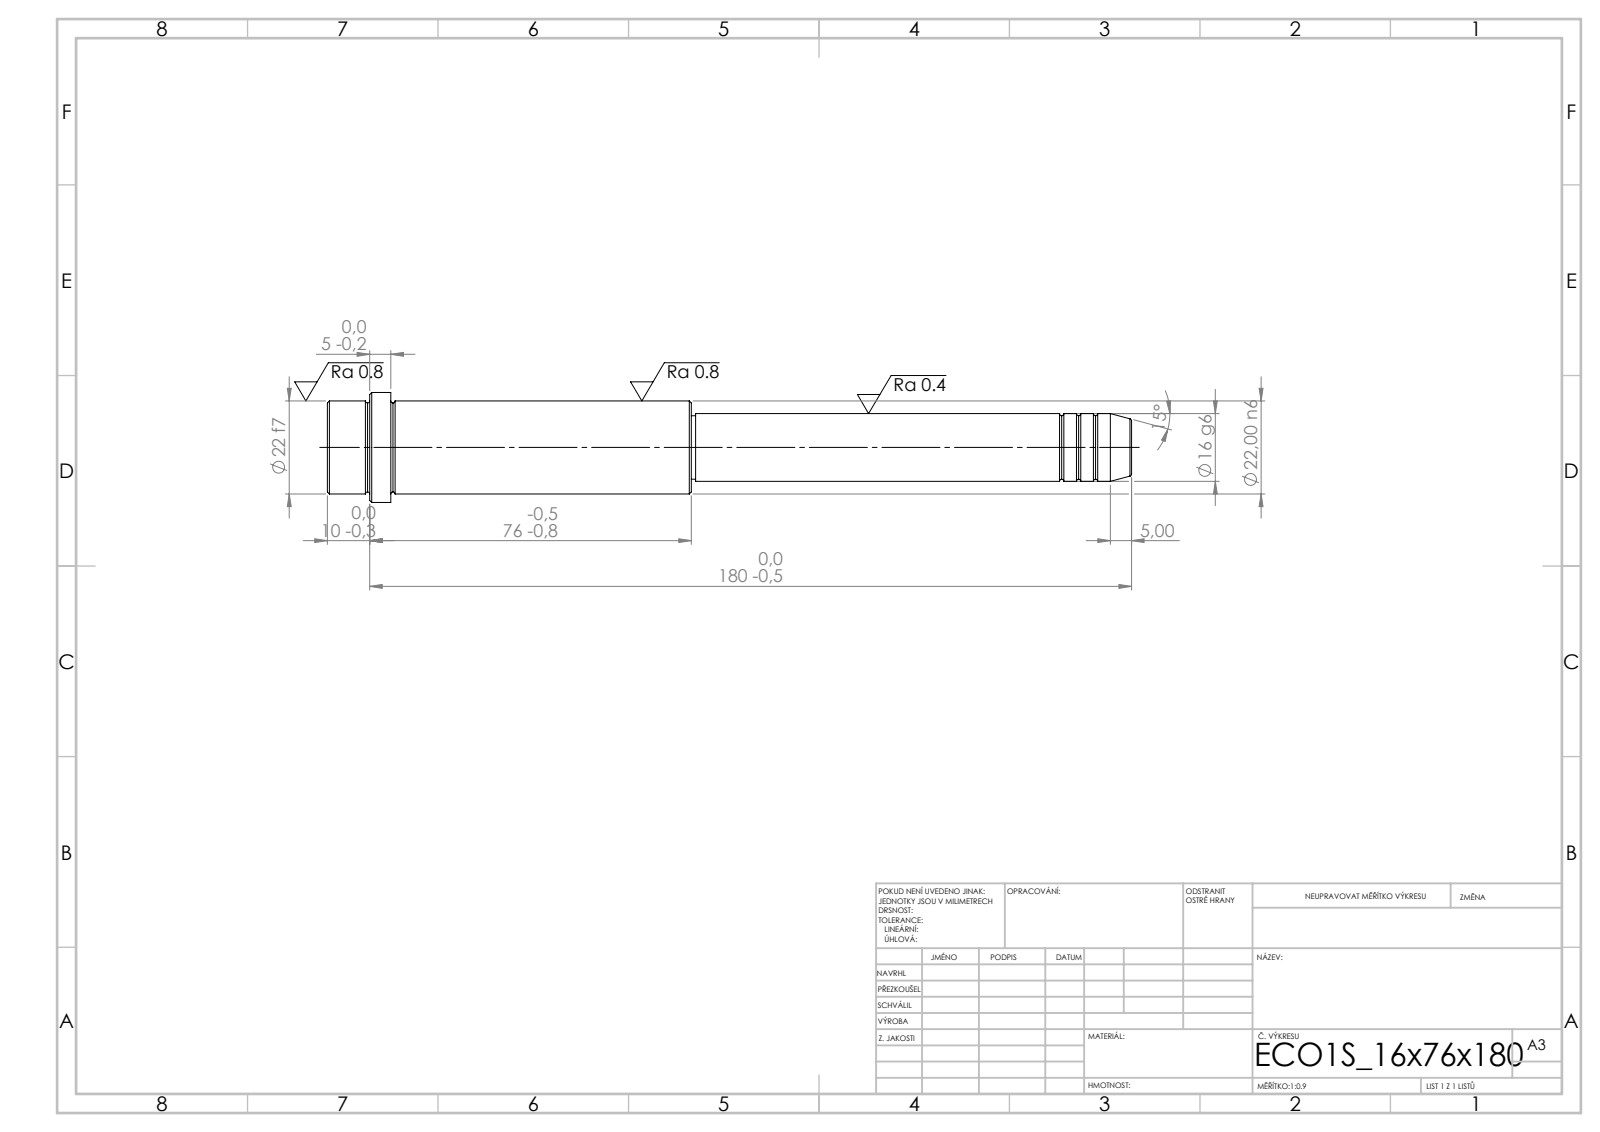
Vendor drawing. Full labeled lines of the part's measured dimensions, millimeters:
STEP written by: SolidWorks 2019 (CONFIG_CONTROL_DESIGN)
Units: millimetres
Bodies: 1 solid, 52 faces (6 planar, 16 cylindrical, 30 other)
Overall size (bounding box): 190 × 26 × 26
Volume: 54 033 mm³ · Surface area: 12 346 mm²
Round bosses / shafts (diameter × count): ⌀26 ×1, ⌀22 ×1, ⌀16 ×1, ⌀15 ×1
Main face-to-face distances: 86, 71, 15, 104, 175, 190, 180, 76, 5, 10
